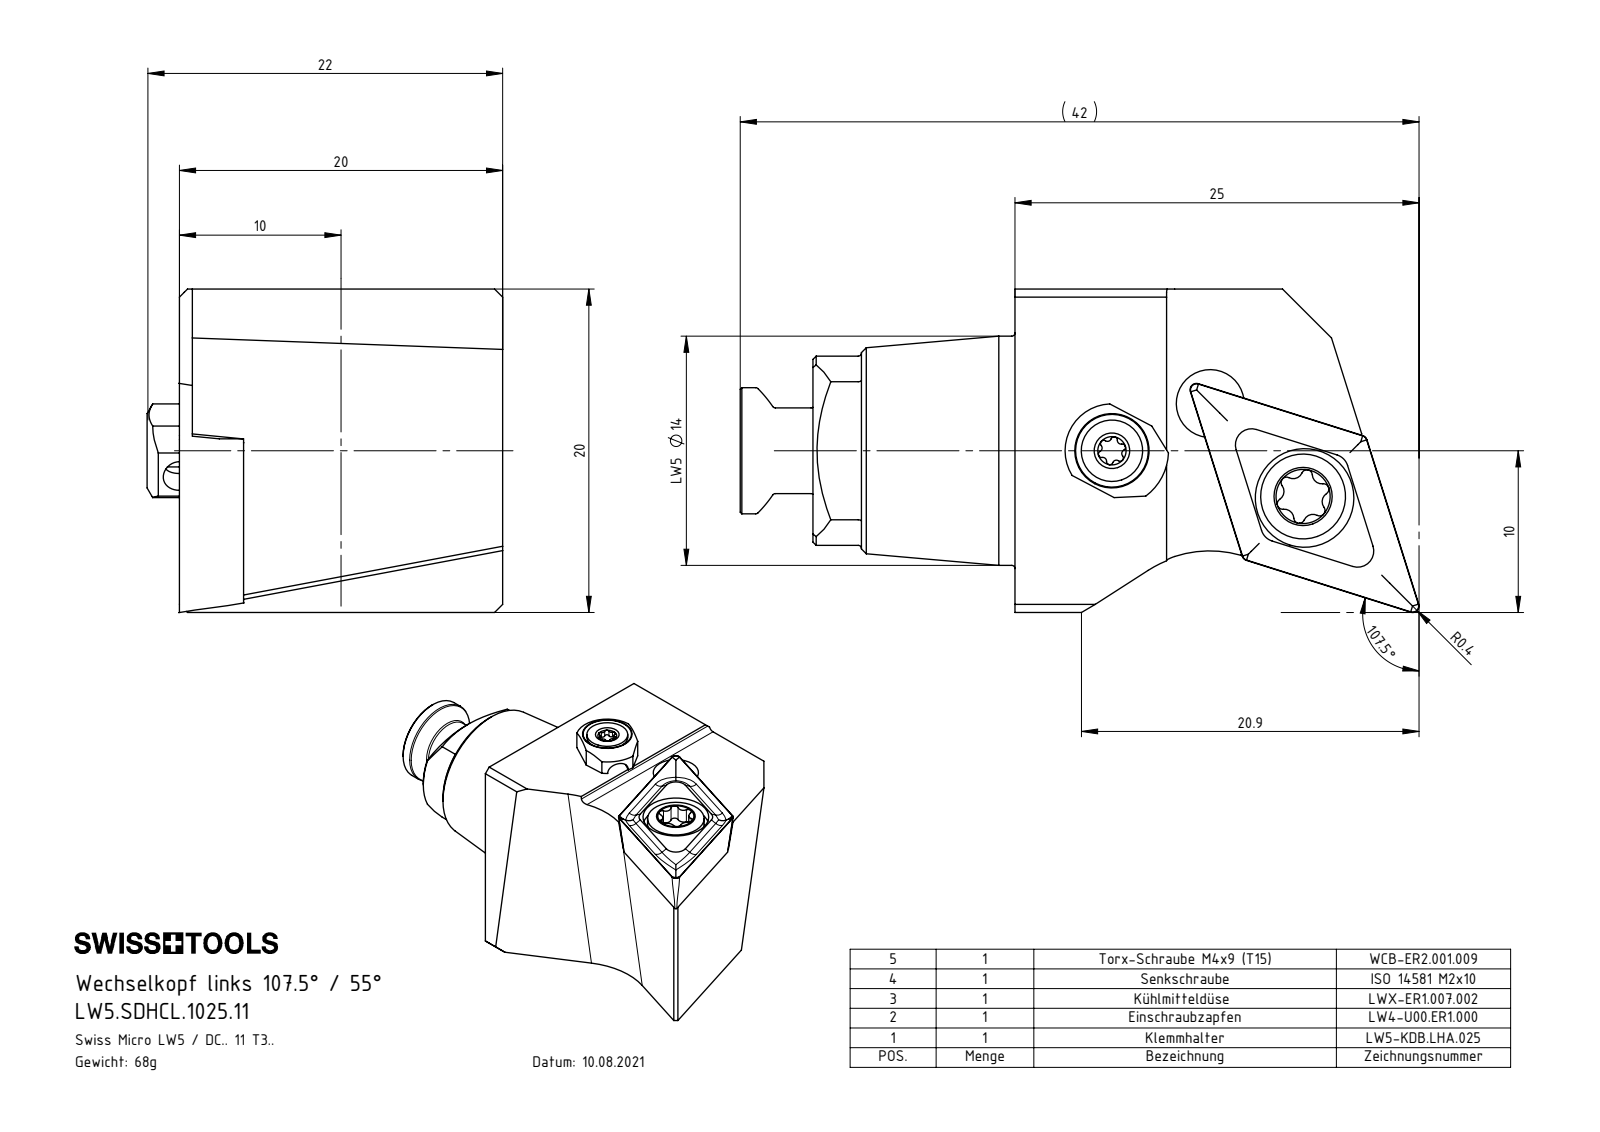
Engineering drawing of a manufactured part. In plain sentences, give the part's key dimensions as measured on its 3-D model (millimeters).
The part is named "WCB-ER2.001.009_A; ISO 14581 - M2x10; LW5.SDHCL.1025.11; LW4-U00.ER1.000_B (+3 more)". Its 3-D file was written by "SolidWorks 2022 (CONFIG_CONTROL_DESIGN)". It is 6 solids with 262 faces: 70 planar, 81 cylindrical and 111 other. Overall it measures 42.01 by 22 by 20 millimeters. Its volume is 8 354 cubic millimeters and its surface area 4 330 square millimeters. Round holes: 2 of diameter 2, 1 of diameter 1.6, 1 of diameter 2.5, 1 of diameter 3, 1 of diameter 3.3, 1 of diameter 4.2, 1 of diameter 4.4, 1 of diameter 5.5, 1 of diameter 6.1. Round bosses or shafts: 1 of diameter 14.17, 1 of diameter 7.7, 1 of diameter 6, 1 of diameter 5.3, 1 of diameter 5.25, 1 of diameter 5, 1 of diameter 4, 1 of diameter 3.8. Partial cylindrical surfaces (rounded edges, fillets, slot ends): 8 of radius 0.2, 6 of radius 0.24, 6 of radius 0.34, 6 of radius 0.59, 1 of radius 0.5, 1 of radius 1, 1 of radius 2.9, 1 of radius 3.5. The main face-to-face distances are 20, 16.03, 3.97, 19.2, 3.17, 0.8, 7.5, 2, 3, 12.5. The hole center spacings are 6.39, 8.13, 8.26, 11.78, 11.88.
